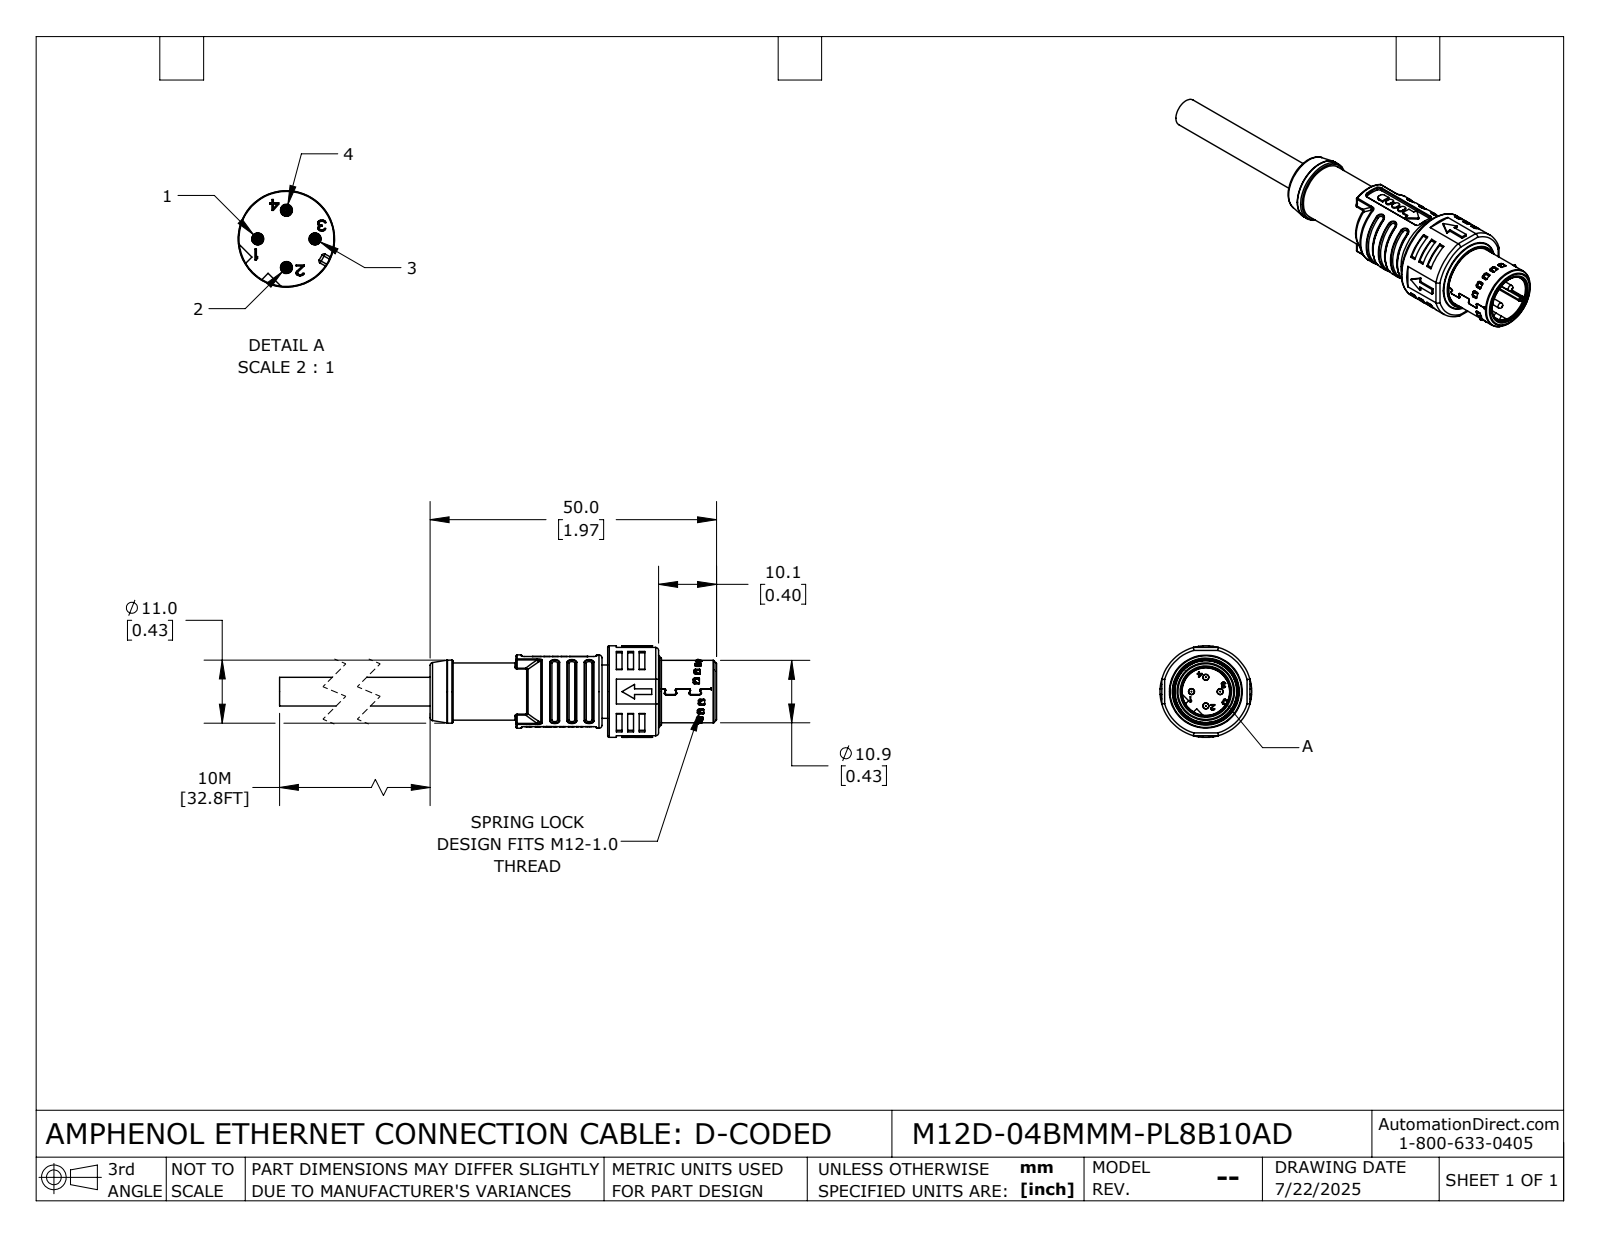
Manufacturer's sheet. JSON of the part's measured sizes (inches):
{"part_name": "M12D-04BMMM-PL8B10AD", "step_written_by": "SolidWorks 2024 (CONFIG_CONTROL_DESIGN)", "units": "inches", "bodies": {"solids": 1, "faces": 2139, "planar": 996, "cylindrical": 644, "other": 499}, "overall_size": [3.15, 0.63, 0.63], "volume_in3": 0.329, "surface_area_in2": 9.24, "round_holes": [[0.041, 4], [0.327, 1], [0.354, 1], [0.4, 1], [0.413, 1], [0.429, 1], [0.453, 1], [0.465, 1], [0.559, 1]], "round_bosses_or_shafts": [[0.039, 4], [0.63, 1], [0.555, 1], [0.504, 1], [0.488, 1], [0.433, 1], [0.411, 1], [0.409, 1]], "partial_cylinders_radius": [[0.008, 119], [0.01, 66], [0.012, 64], [0.006, 44], [0.02, 38], [0.005, 12], [0.028, 11], [0.004, 7]], "face_to_face_distances": [0.039, 1.181, 0.398, 0.35, 0.098, 0.047, 0.339, 1.28, 0.606, 0.059], "hole_center_spacings": [0.098, 0.139, 0.197]}
